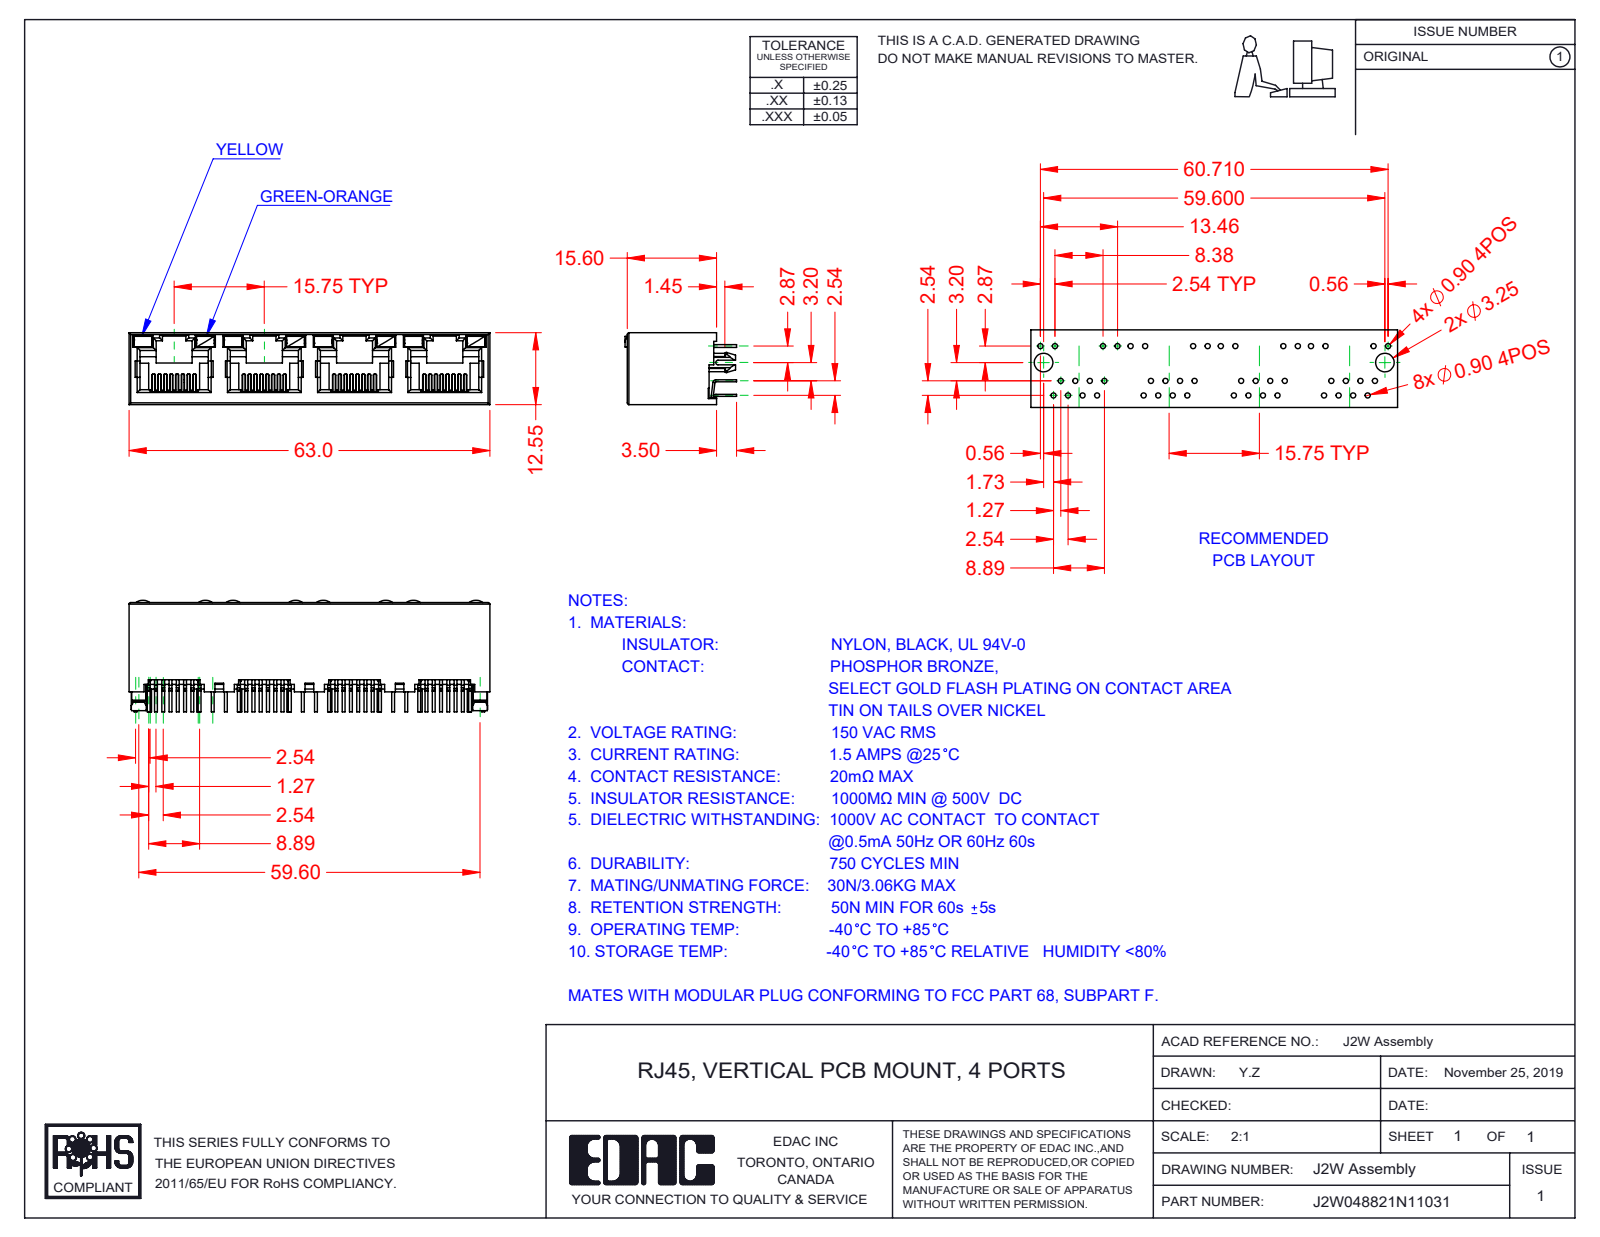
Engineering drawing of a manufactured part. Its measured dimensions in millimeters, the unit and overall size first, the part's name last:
Units: millimetres
Overall size (bounding box): 63 × 19.5 × 12.55
Partial cylindrical surfaces — rounded edges, fillets, slot ends (radius × count): R0.15 ×64, R0.2 ×29, R0.5 ×28, R0.3 ×14, R0.45 ×8, R2 ×8, R0.25 ×2, R1.5 ×2
Main face-to-face distances: 12.55, 11.9, 0.65, 15.75, 0.36, 1.5, 0.78, 0.6, 11.3, 31.5
Volume: 5 335 mm³ · Surface area: 13 144 mm²
Bodies: 45 solids, 3139 faces (2600 planar, 481 cylindrical, 58 other)
Part name (STEP PRODUCT): J2W048821N17131; 2W Insulator; 2W LED RH_7-Green-Orange; 2W Contacts (+2 more)
STEP written by: SolidWorks 2016 (CONFIG_CONTROL_DESIGN)
